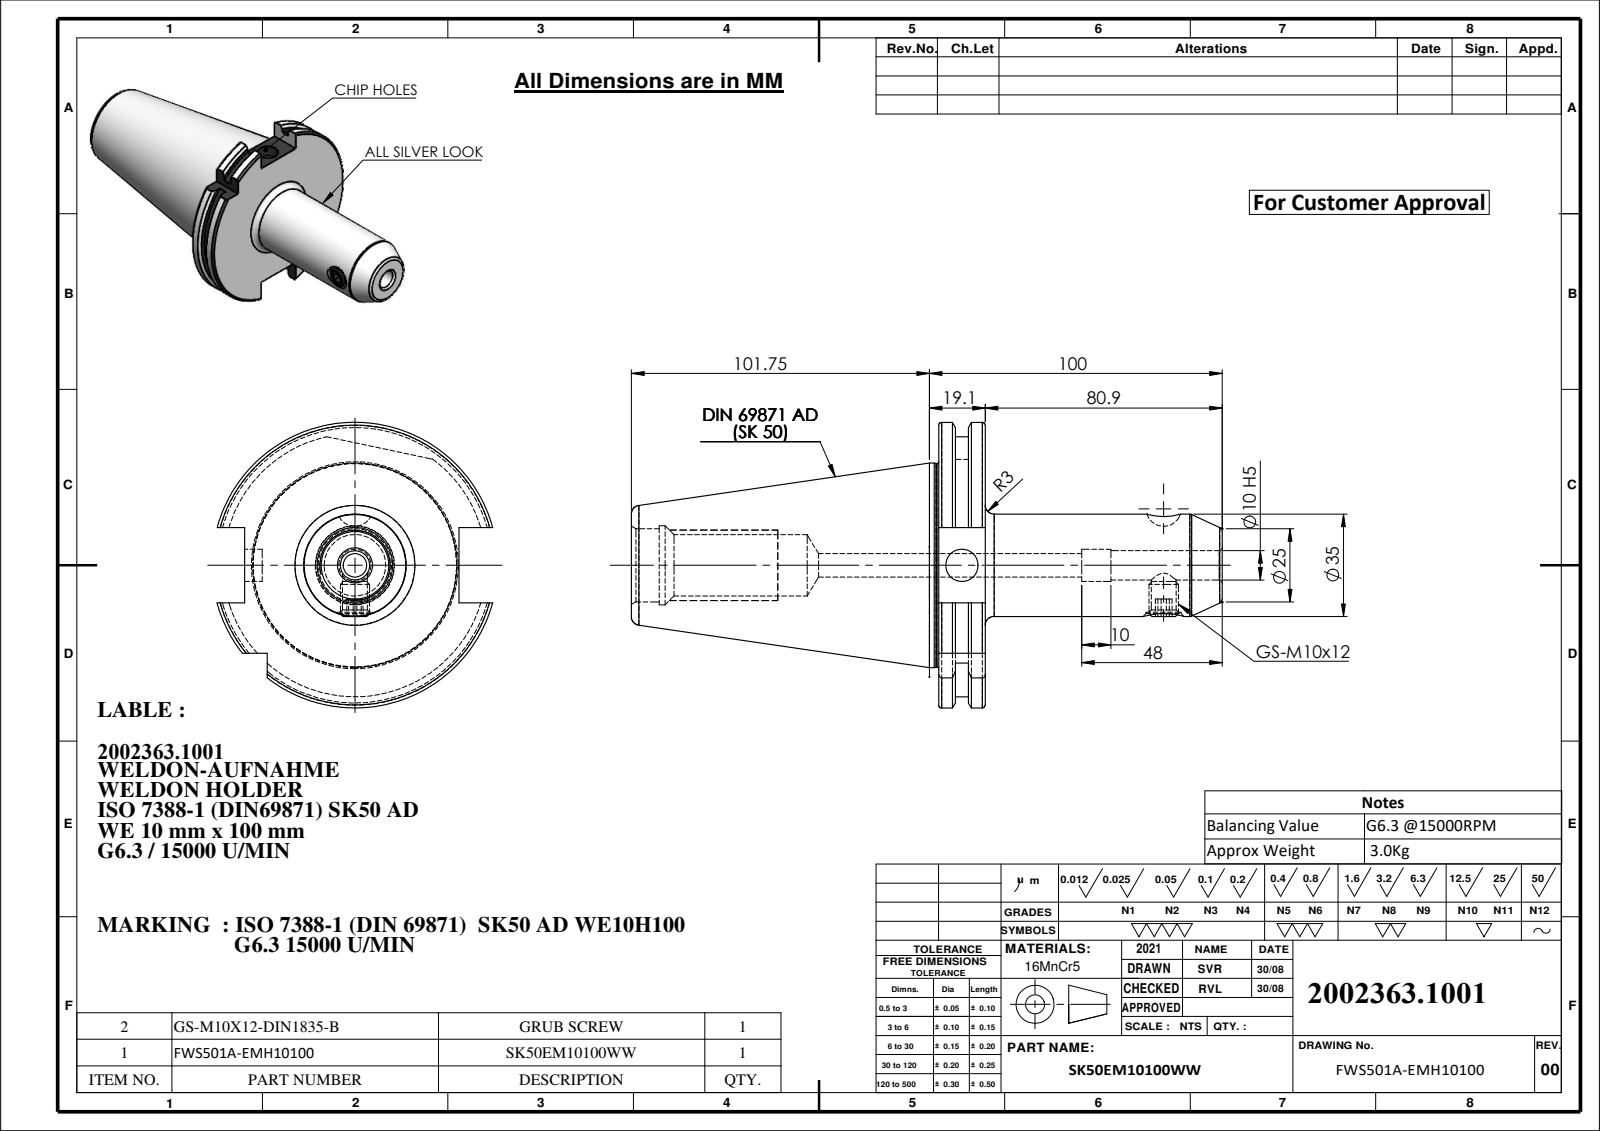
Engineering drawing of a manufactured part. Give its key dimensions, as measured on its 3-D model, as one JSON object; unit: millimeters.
{"part_name": "FWS501A-EMH10100; GS-M10X12-DIN1835-B; SK50EM10100WW; SK50EM10100WW_ISO", "step_written_by": "SolidWorks 2024 (CONFIG_CONTROL_DESIGN)", "units": "millimeters", "bodies": {"solids": 2, "faces": 125, "planar": 33, "cylindrical": 39, "other": 53}, "overall_size": [201.75, 97.5, 94.05], "volume_mm3": 405812, "surface_area_mm2": 53429, "round_holes": [[11, 2], [8, 1], [8.5, 1], [10, 1], [12, 1], [21, 1], [25, 1], [27, 1]], "round_bosses_or_shafts": [[69.85, 1], [69.45, 1], [35, 1], [10, 1]], "partial_cylinders_radius": [[44.9, 1], [48.75, 1]], "face_to_face_distances": [15.9, 5.66, 10.24, 10.15, 4.49, 5.75, 104.95, 110.61, 115.1, 120.85]}
